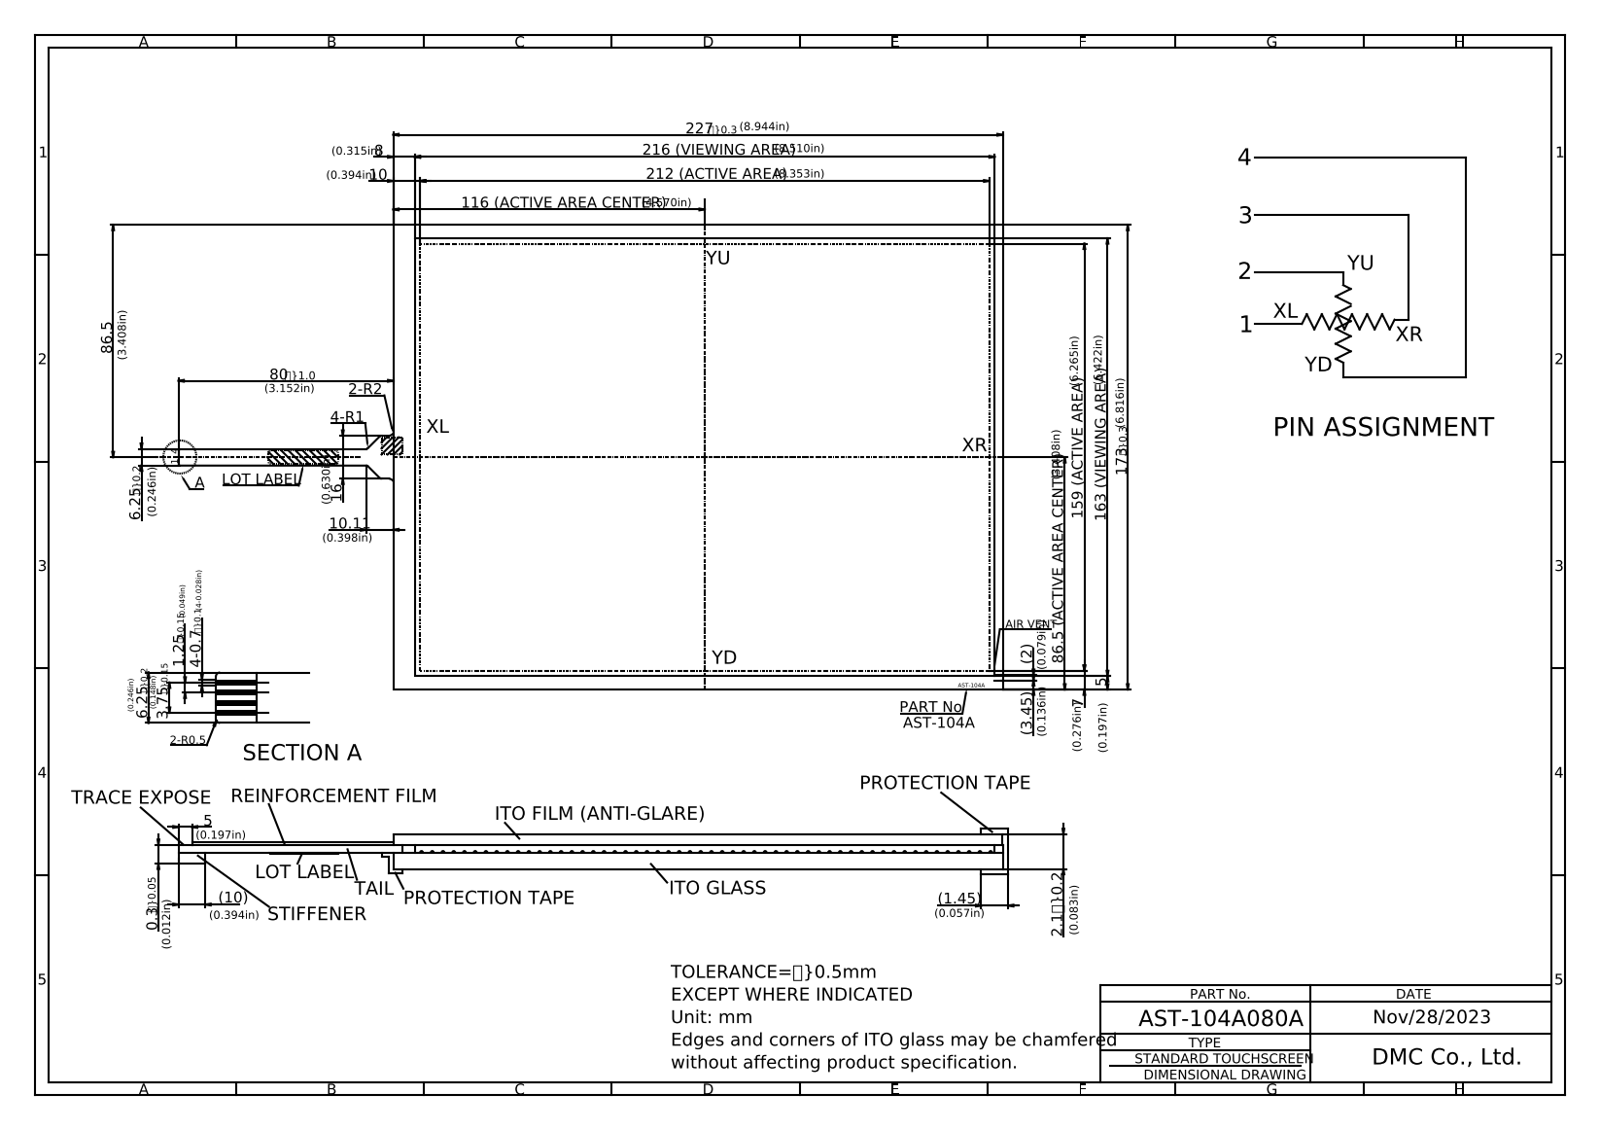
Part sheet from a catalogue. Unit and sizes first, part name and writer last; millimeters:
Units: millimetres
Overall size (bounding box): 352.4 × 242.2 × 2.1
Partial cylindrical surfaces — rounded edges, fillets, slot ends (radius × count): R1 ×4, R0.5 ×2
Main face-to-face distances: 2.1, 2, 1.9, 1.8, 173, 227, 1.5, 0.4, 0.5, 0.6
Volume: 82 391 mm³ · Surface area: 81 529 mm²
Bodies: 1 solid, 51 faces (45 planar, 6 cylindrical, 0 other)
Part name (STEP PRODUCT): AST-104A080A
STEP written by: Autodesk Inventor 2020 (CONFIG_CONTROL_DESIGN)
